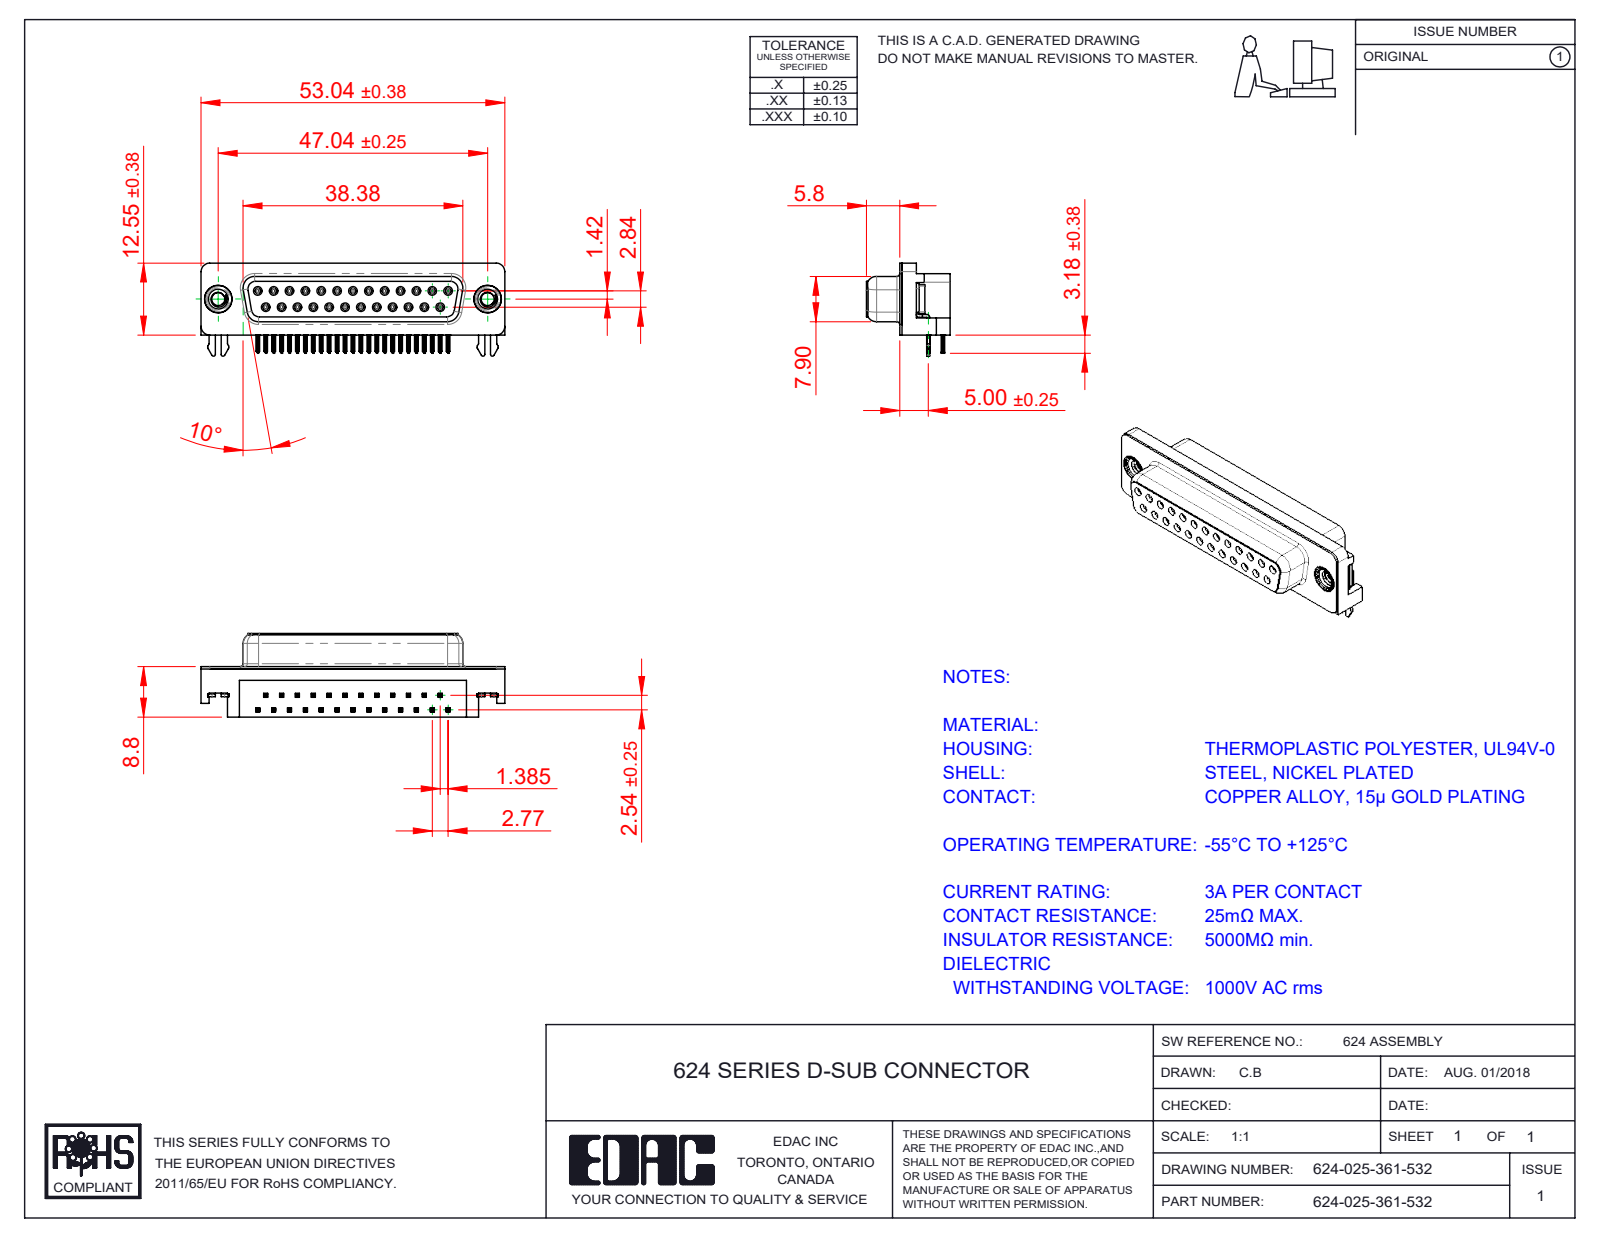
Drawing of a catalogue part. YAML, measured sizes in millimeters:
part_name: "624 2 Prong Board Lock; 624 Socket Bottom; 624 Housing_25 Socket; 624-025-361-532 (+3 more)"
step_written_by: "SolidWorks 2016 (CONFIG_CONTROL_DESIGN)"
units: millimeters
bodies: {solids: 31, faces: 3752, planar: 1630, cylindrical: 914, other: 1208}
overall_size: [53.04, 16.25, 14.6]
volume: 5963
surface_area: 8277
round_holes:
  - {diameter: 0.8, count: 25}
  - {diameter: 0.9, count: 25}
  - {diameter: 2.26, count: 2}
  - {diameter: 4, count: 2}
  - {diameter: 4.8, count: 2}
  - {diameter: 5, count: 2}
round_bosses_or_shafts:
  - {diameter: 1.2, count: 25}
  - {diameter: 4.9, count: 2}
  - {diameter: 4.75, count: 2}
  - {diameter: 3.9, count: 2}
partial_cylinders:
  - {radius: 0.1, count: 200}
  - {radius: 0.15, count: 100}
  - {radius: 0.35, count: 50}
  - {radius: 0.34, count: 25}
  - {radius: 0.28, count: 12}
  - {radius: 0.5, count: 10}
  - {radius: 1, count: 10}
  - {radius: 0.25, count: 8}
face_to_face_distances: [0.4, 6.2, 8.4, 3.18, 9.38, 8.8, 2.73, 2.9, 0.85, 7.05]
hole_center_spacings: [3.16, 2.77, 5.54, 8.31, 11.08, 5.03, 5.04, 7.48]
